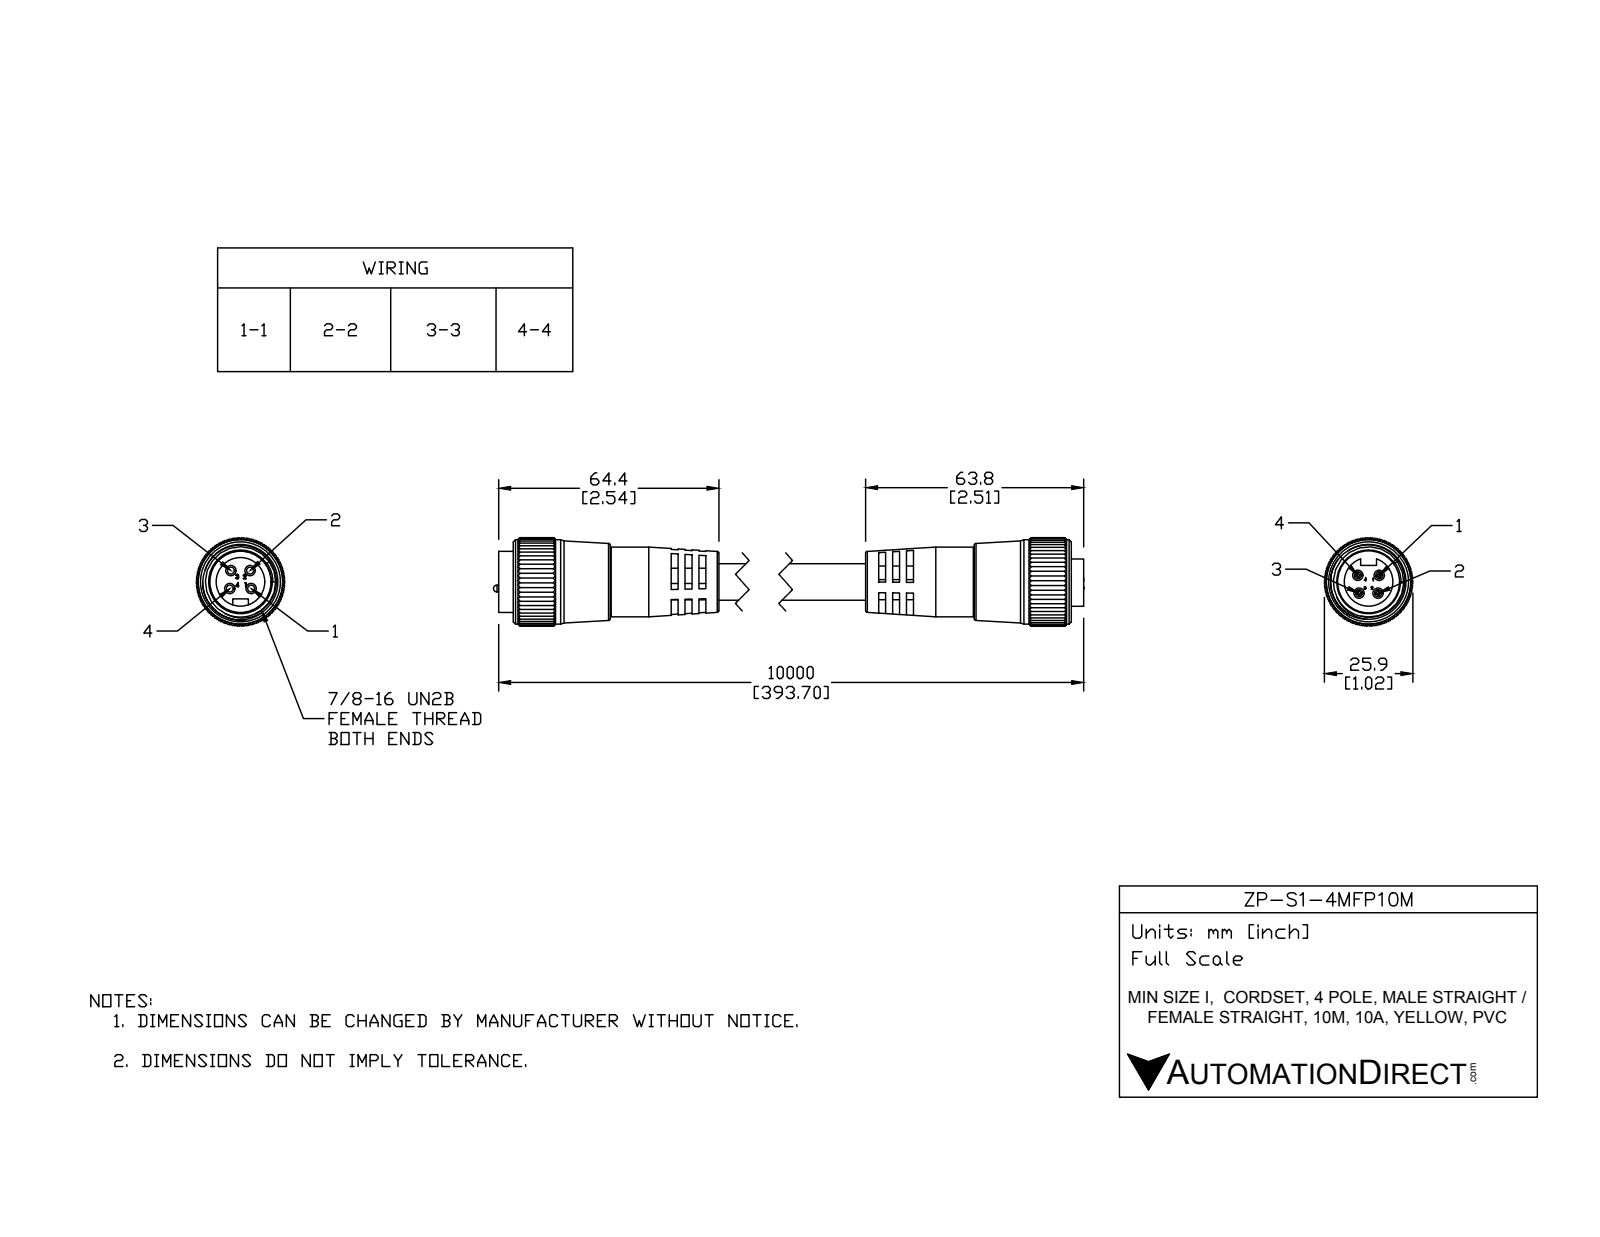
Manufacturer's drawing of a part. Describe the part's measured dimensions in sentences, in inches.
The part is named "ZP-S1-4MFP-10M". Its 3-D file was written by "SolidWorks 2015 (AUTOMOTIVE_DESIGN)". It is 8 solids with 1142 faces: 422 planar, 624 cylindrical and 96 other. Overall it measures 9.042 by 1.017 by 1.017 inches. Its volume is 3.102 cubic inches and its surface area 36.25 square inches. Round holes: 4 of diameter 0.12, 1 of diameter 0.786, 1 of diameter 0.805, 1 of diameter 0.827. Round bosses or shafts: 4 of diameter 0.12, 4 of diameter 0.079, 1 of diameter 0.972, 1 of diameter 0.803, 1 of diameter 0.768, 1 of diameter 0.704, 1 of diameter 0.56, 1 of diameter 0.39. Partial cylindrical surfaces (rounded edges, fillets, slot ends): 165 of radius 0.01, 1 of radius 0.09, 1 of radius 0.207, 1 of radius 0.509. The main face-to-face distances are 0.079, 0.158, 4.633, 4.474, 0.159, 4.95, 2.356, 0.159, 4.791, 4.792. The hole center spacings are 0.144, 0.206, 0.17, 0.17, 0.22, 0.246, 0.311, 0.311.
